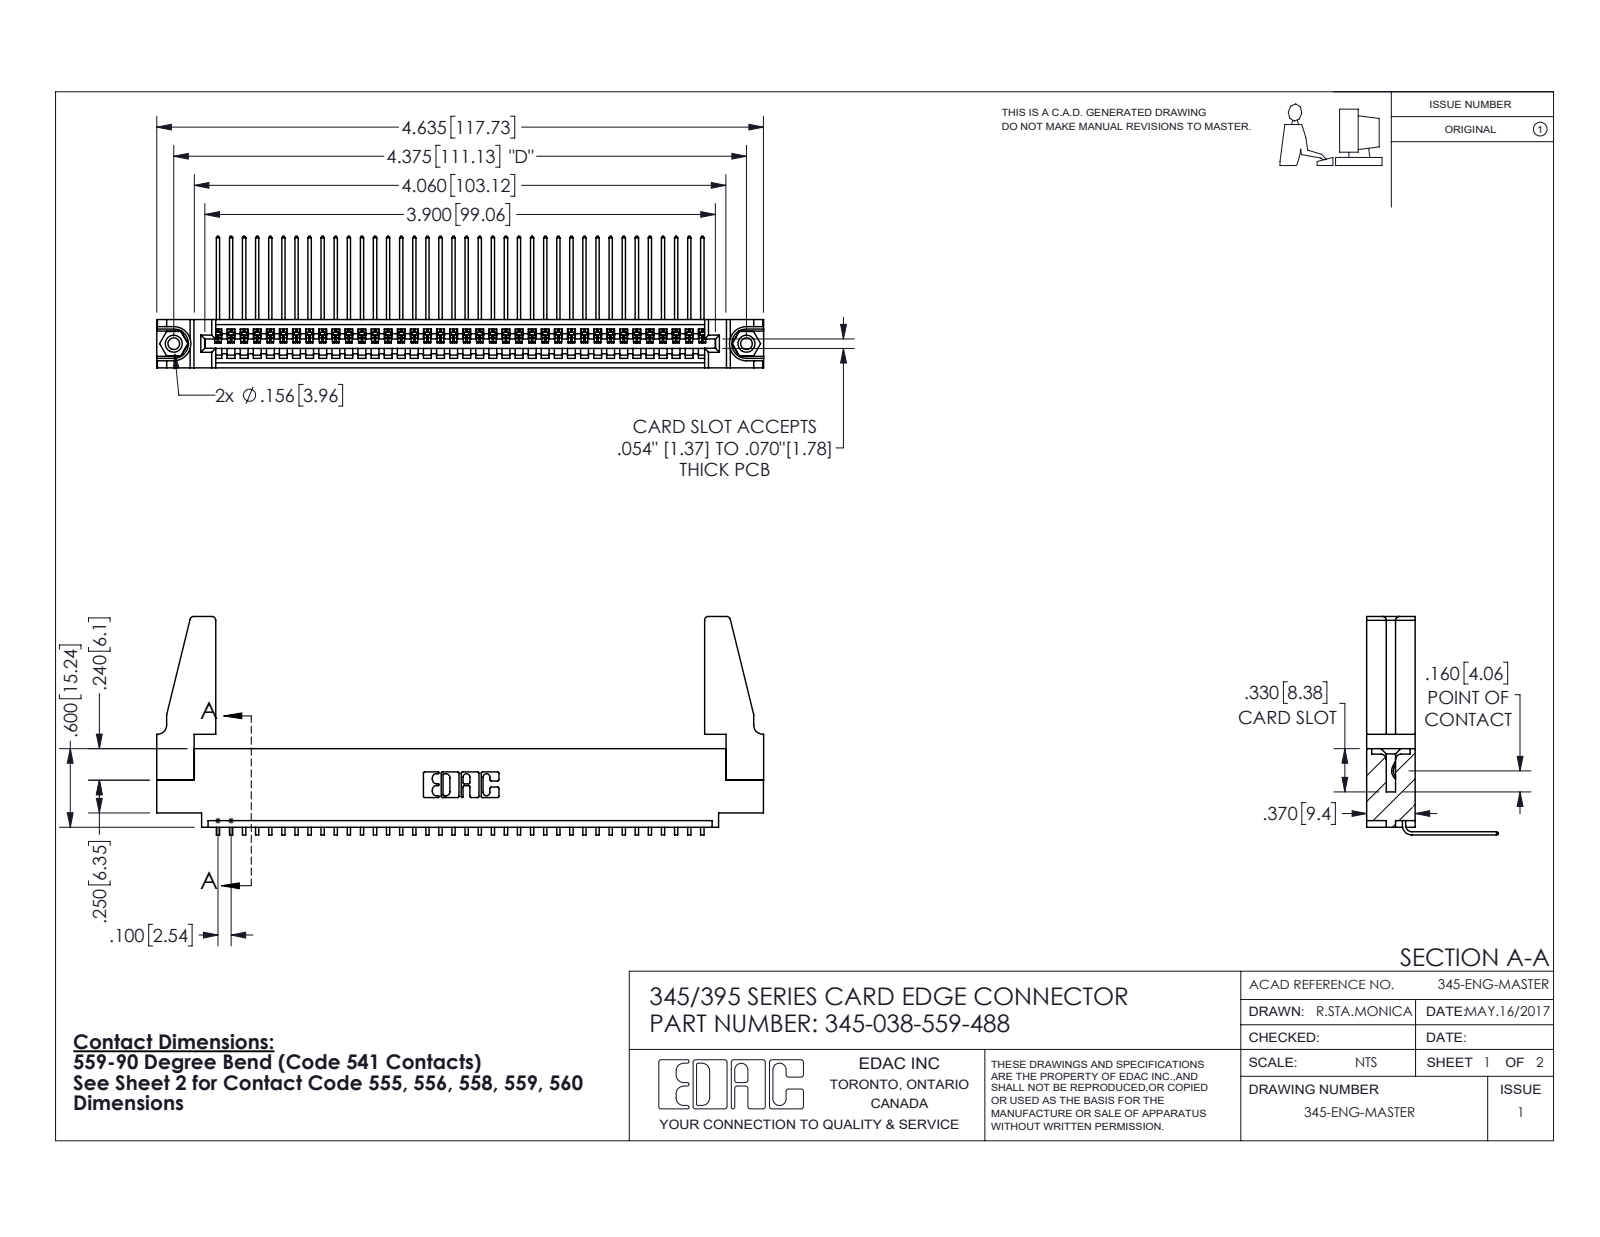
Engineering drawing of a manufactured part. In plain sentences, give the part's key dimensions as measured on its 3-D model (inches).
The part is named "345-250-001_345-250-001-102; 345-292-001_558 559 Tail - 1; 345-220-078_345-220-088; 345 Part_0.110 Offset - 0.156 Dia-TH (+1 more)". Its 3-D file was written by "SolidWorks 2016 (CONFIG_CONTROL_DESIGN)". It is 43 solids with 2534 faces: 1752 planar, 766 cylindrical and 16 other. Overall it measures 4.636 by 1.669 by 1.005 inches. Its volume is 0.882 cubic inches and its surface area 29.13 square inches. Round holes: 2 of diameter 0.089, 2 of diameter 0.125, 2 of diameter 0.156, 1 of diameter 0.064. Round bosses or shafts: 2 of diameter 0.155. Partial cylindrical surfaces (rounded edges, fillets, slot ends): 76 of radius 0.006, 22 of radius 0.01, 8 of radius 0.03, 6 of radius 0.007, 6 of radius 0.031, 3 of radius 0.026, 2 of radius 0.031, 2 of radius 0.04. The main face-to-face distances are 0.072, 0.37, 0.298, 0.2, 0.098, 0.272, 0.025, 0.225, 0.149, 0.072. The hole center spacings are 0.27, 4.139, 4.375.
